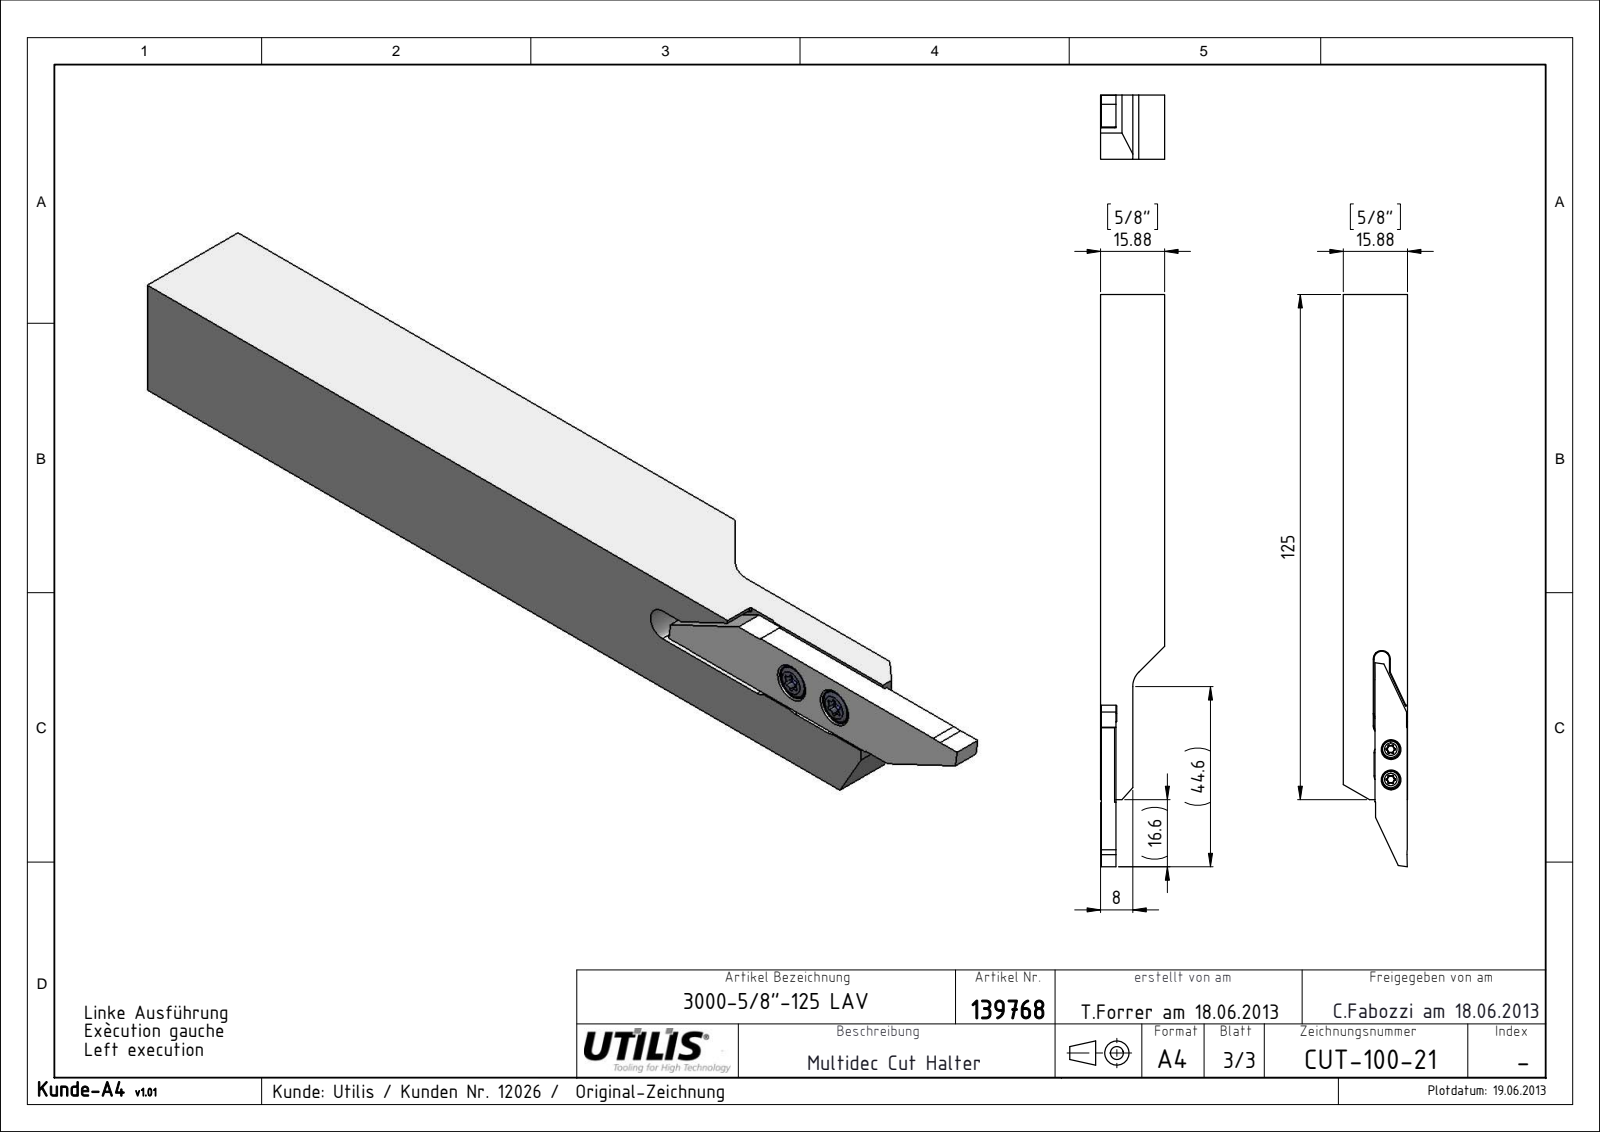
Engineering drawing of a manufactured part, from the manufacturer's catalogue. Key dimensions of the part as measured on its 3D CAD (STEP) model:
Part name (STEP PRODUCT): CUT-100-Kunde_3000-5-8-125 LAV; CUT- 3000 R+L Lang NUR FÜR KUNDEN _L-Lang; MSP-16_M3x7.3 T08; CUT-100-21
STEP written by: SolidWorks 2014 (CONFIG_CONTROL_DESIGN)
Units: millimetres
Bodies: 4 solids, 118 faces (34 planar, 56 cylindrical, 28 other)
Overall size (bounding box): 141.6 × 15.88 × 15.88
Volume: 27 233 mm³ · Surface area: 9 168 mm²
Round holes (diameter × count): ⌀2.5 ×2, ⌀4.9 ×2
Round bosses / shafts (diameter × count): ⌀4.1 ×2, ⌀3 ×2
Partial cylindrical surfaces — rounded edges, fillets, slot ends (radius × count): R0.2 ×12, R0.45 ×12, R2.1 ×4, R10 ×2, R5 ×1
Main face-to-face distances: 15.88, 15.87, 3.79, 12.08, 8, 4.21, 7.87, 3.6, 7.81, 15.68
Hole centre spacings: 3.75, 7.5, 3.65, 3.85, 7.4, 7.6
